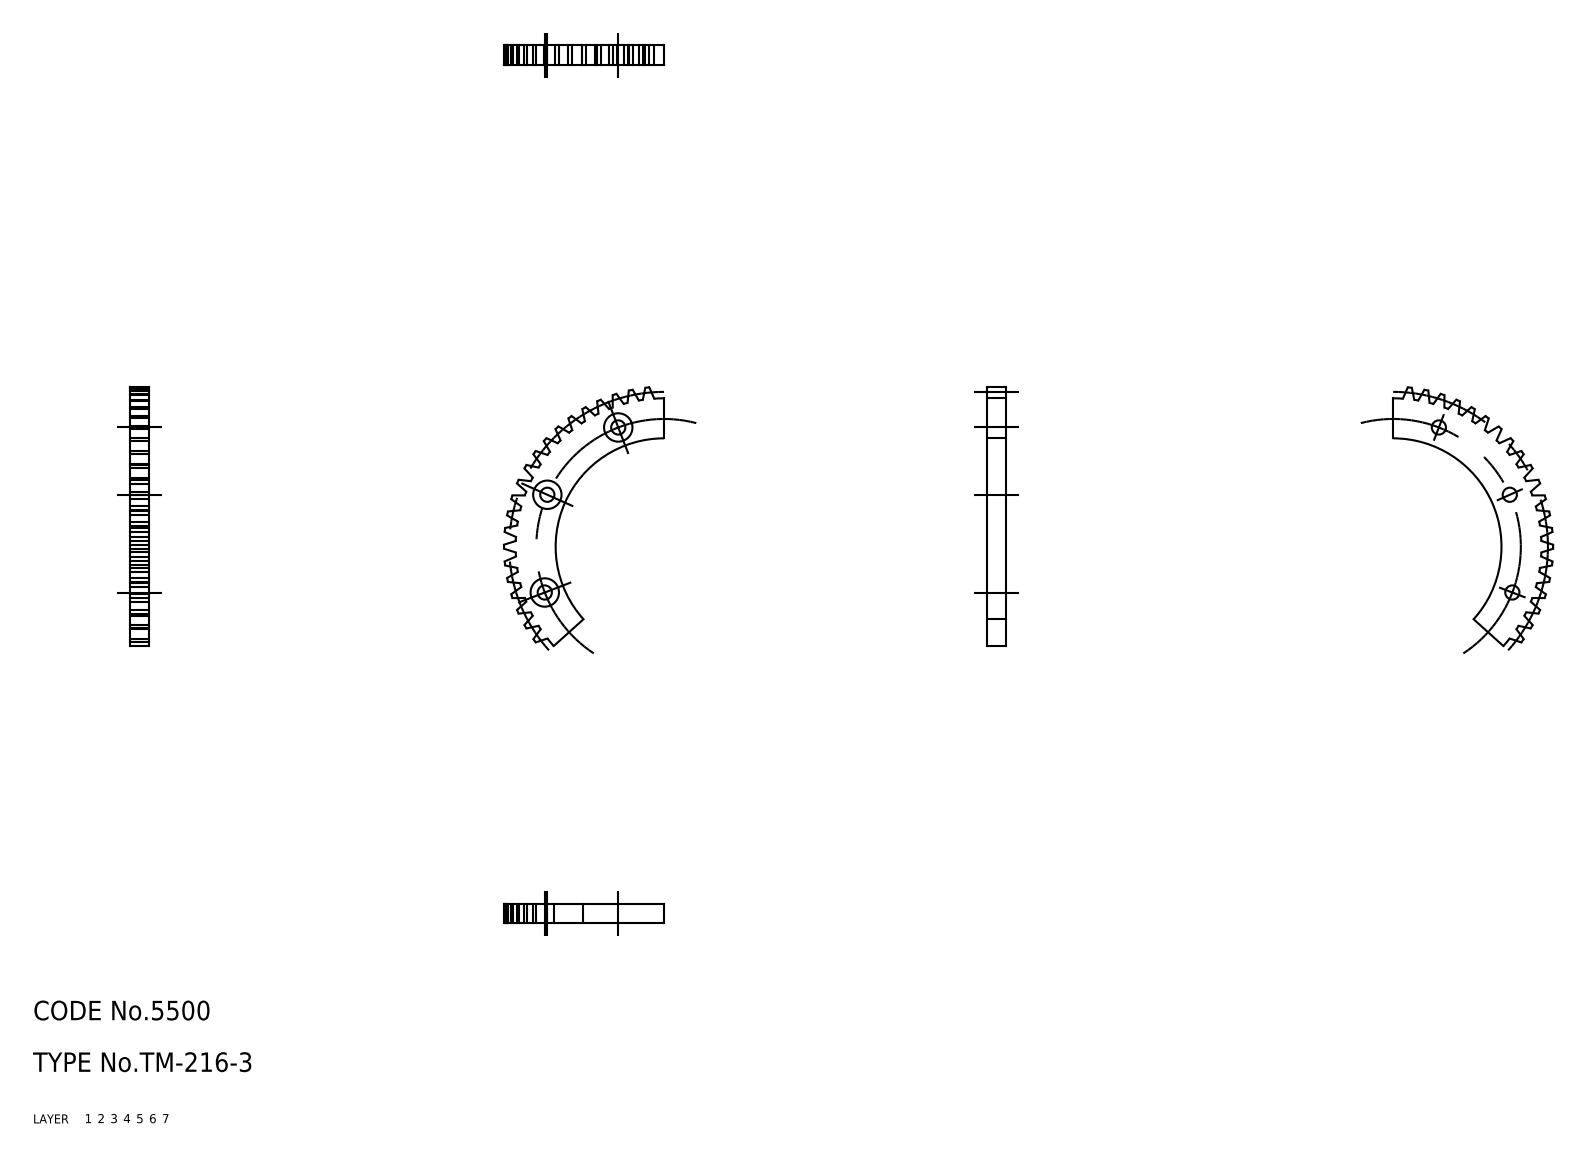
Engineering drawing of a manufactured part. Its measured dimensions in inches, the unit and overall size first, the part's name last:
Units: inches
Overall size (bounding box): 1.578 × 0.976 × 0.118
Volume: 0.057 in³ · Surface area: 1.814 in²
Bodies: 1 solid, 102 faces (0 planar, 0 cylindrical, 102 other)
Part name (STEP PRODUCT): rack
STEP written by: CADfix (AUTOMOTIVE_DESIGN)
